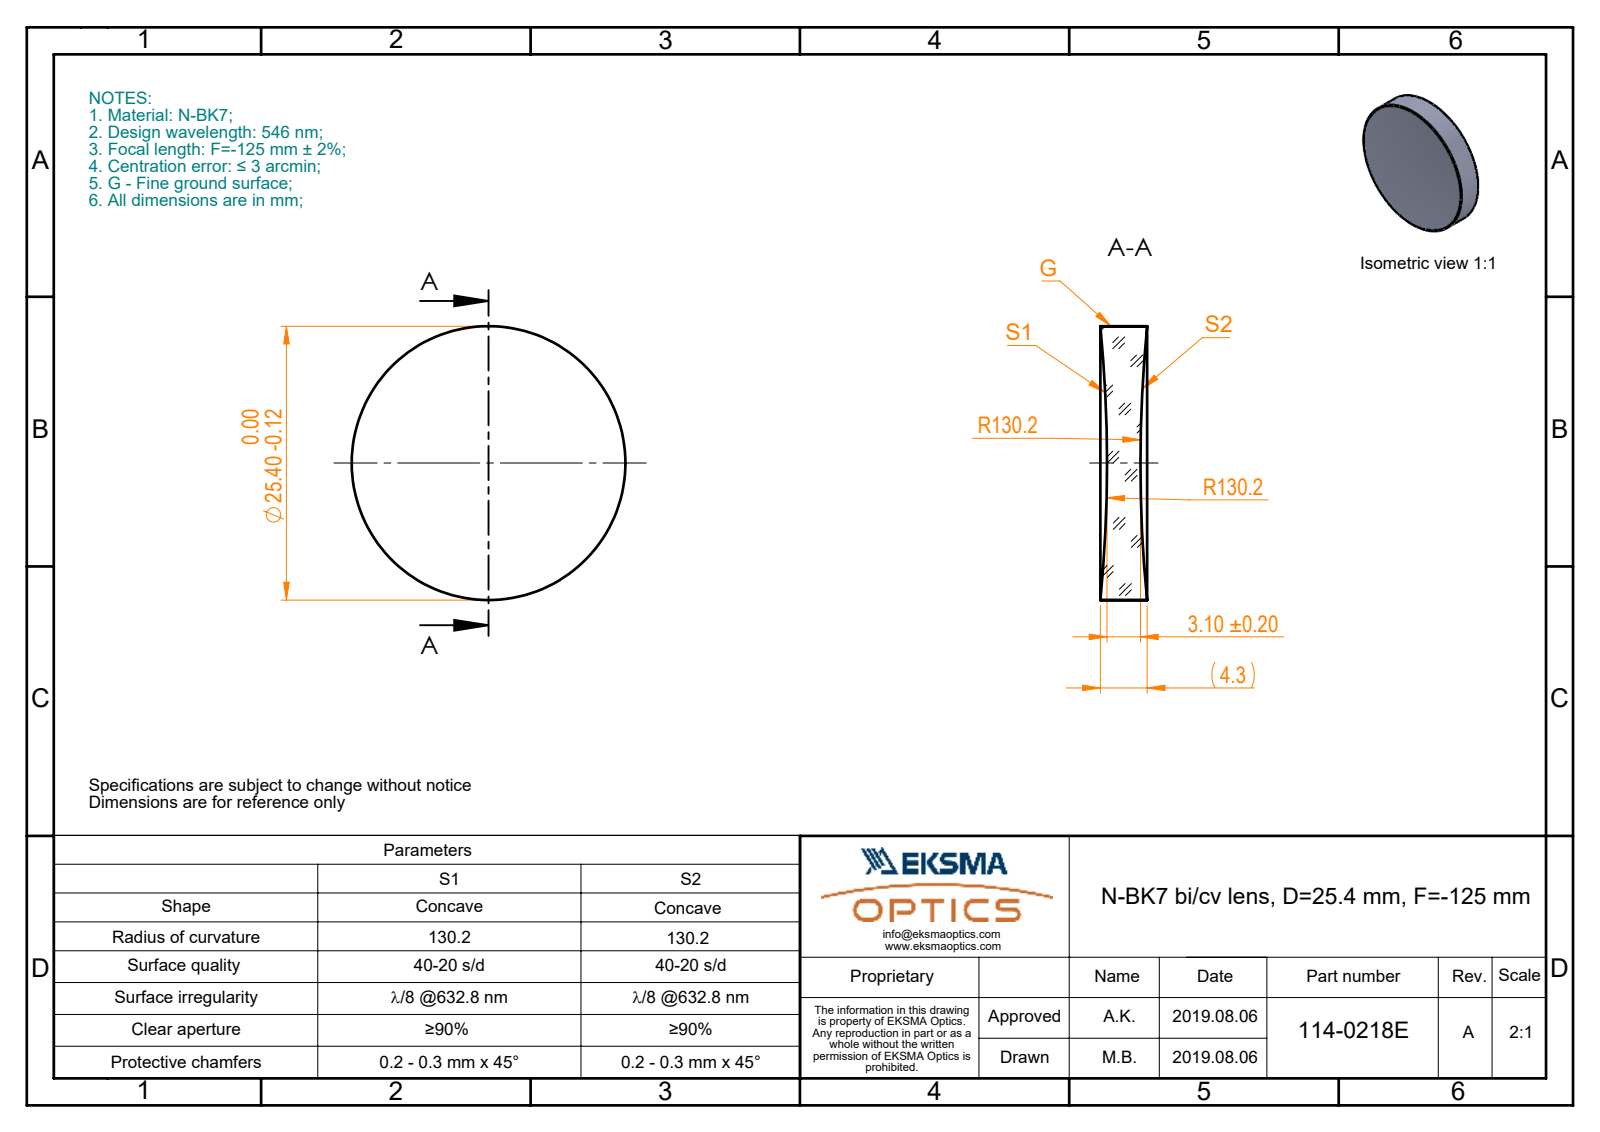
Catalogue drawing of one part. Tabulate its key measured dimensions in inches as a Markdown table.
| quantity | value |
| --- | --- |
| part name | 114-0218E BK7 bi-cv 25.4 F-125 |
| STEP written by | SolidWorks 2017 (CONFIG_CONTROL_DESIGN) |
| units | inches |
| bodies | 1 solid, 6 faces (0 planar, 2 cylindrical, 4 other) |
| overall size | 1 × 1 × 0.171 |
| volume | 0.115 in³ |
| surface area | 2.111 in² |
| round bosses / shafts (diameter × count) | 1 × 1 |
